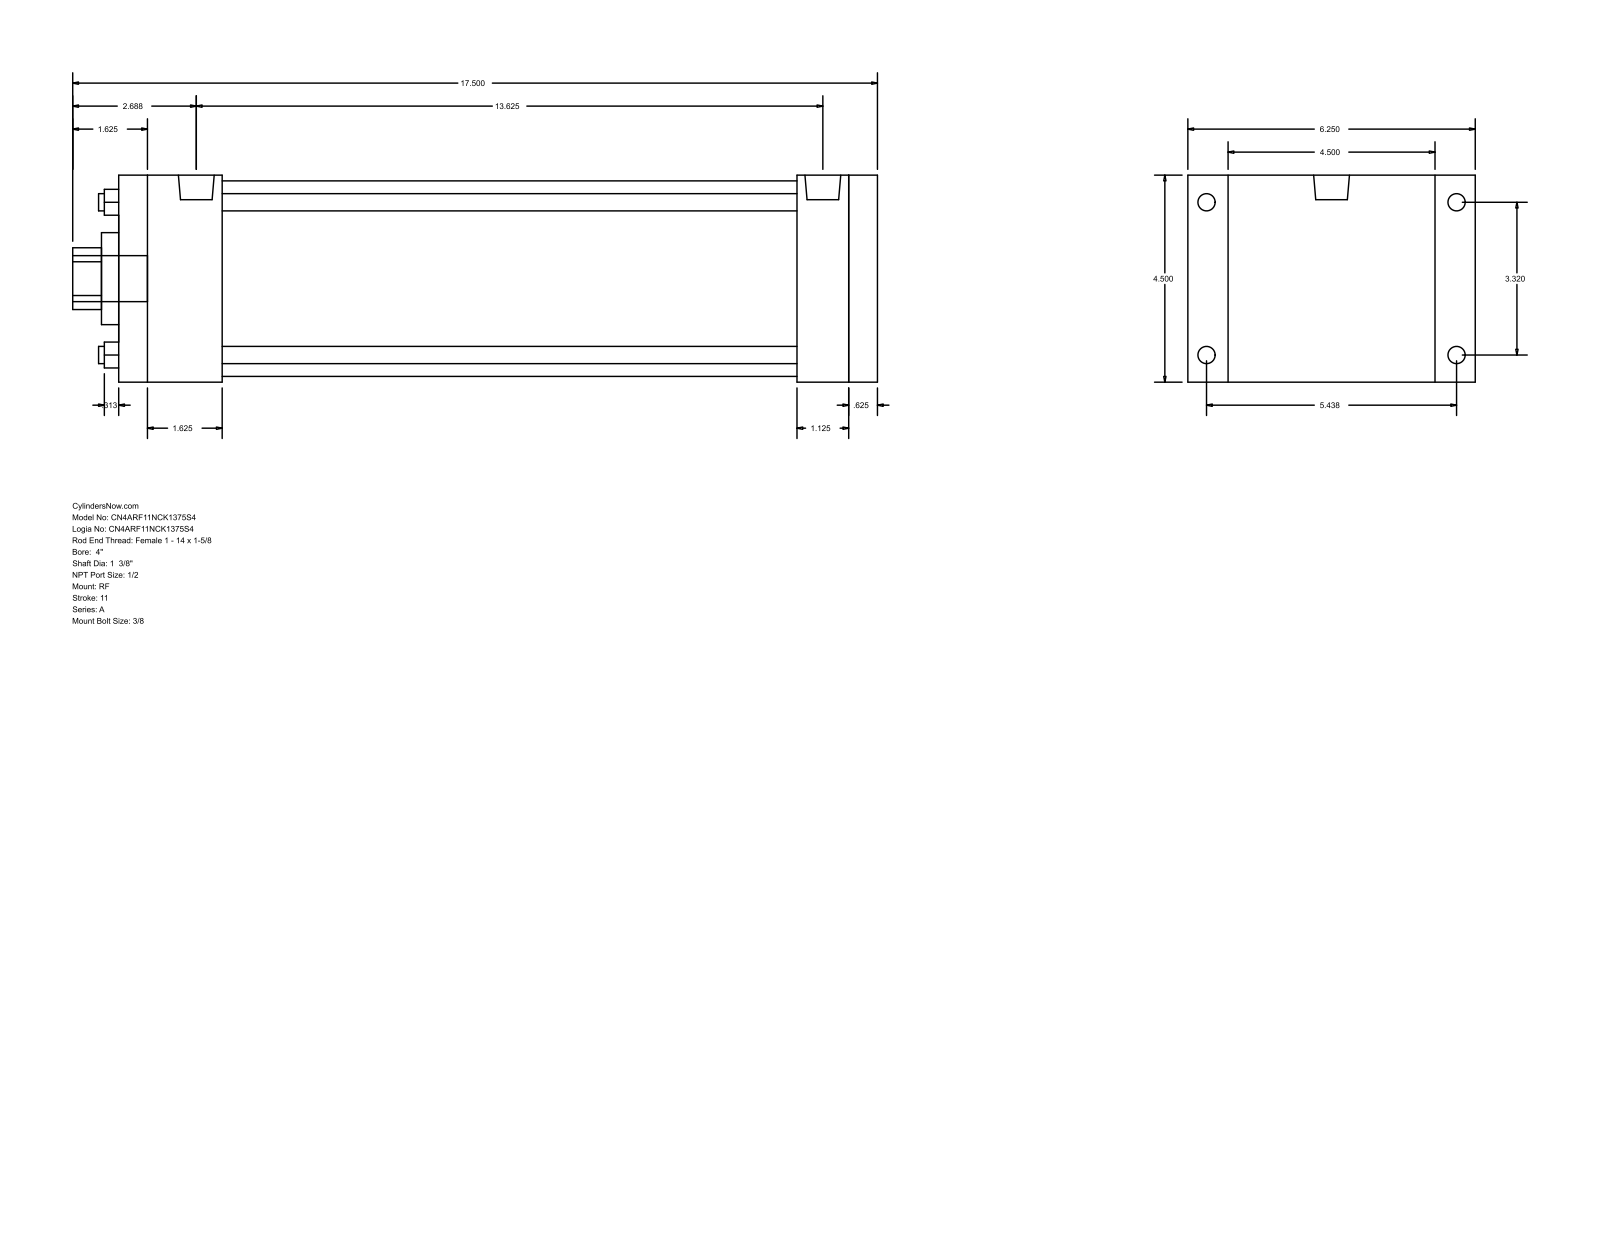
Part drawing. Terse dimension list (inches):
name: A_RF__0400_1.375
written by: GSSL Pune (CONFIG_CONTROL_DESIGN)
unit: in
bodies: 0 solids, 92 faces (64 planar, 28 cylindrical, 0 other)
size: 17.5 × 6.25 × 4.5
holes: 4× ⌀0.375, 1× ⌀1.375, 1× ⌀2, 1× ⌀4.25
bosses: 4× ⌀0.375, 4× ⌀0.344, 2× ⌀0.778, 1× ⌀1
rounds: 1× R0.672
face distances: 4.5, 16.5, 0.625, 15.875, 1.125, 0.875, 5.375, 14.75, 1.75, 2.25
hole spacings: 2.347, 3.32, 4.695
